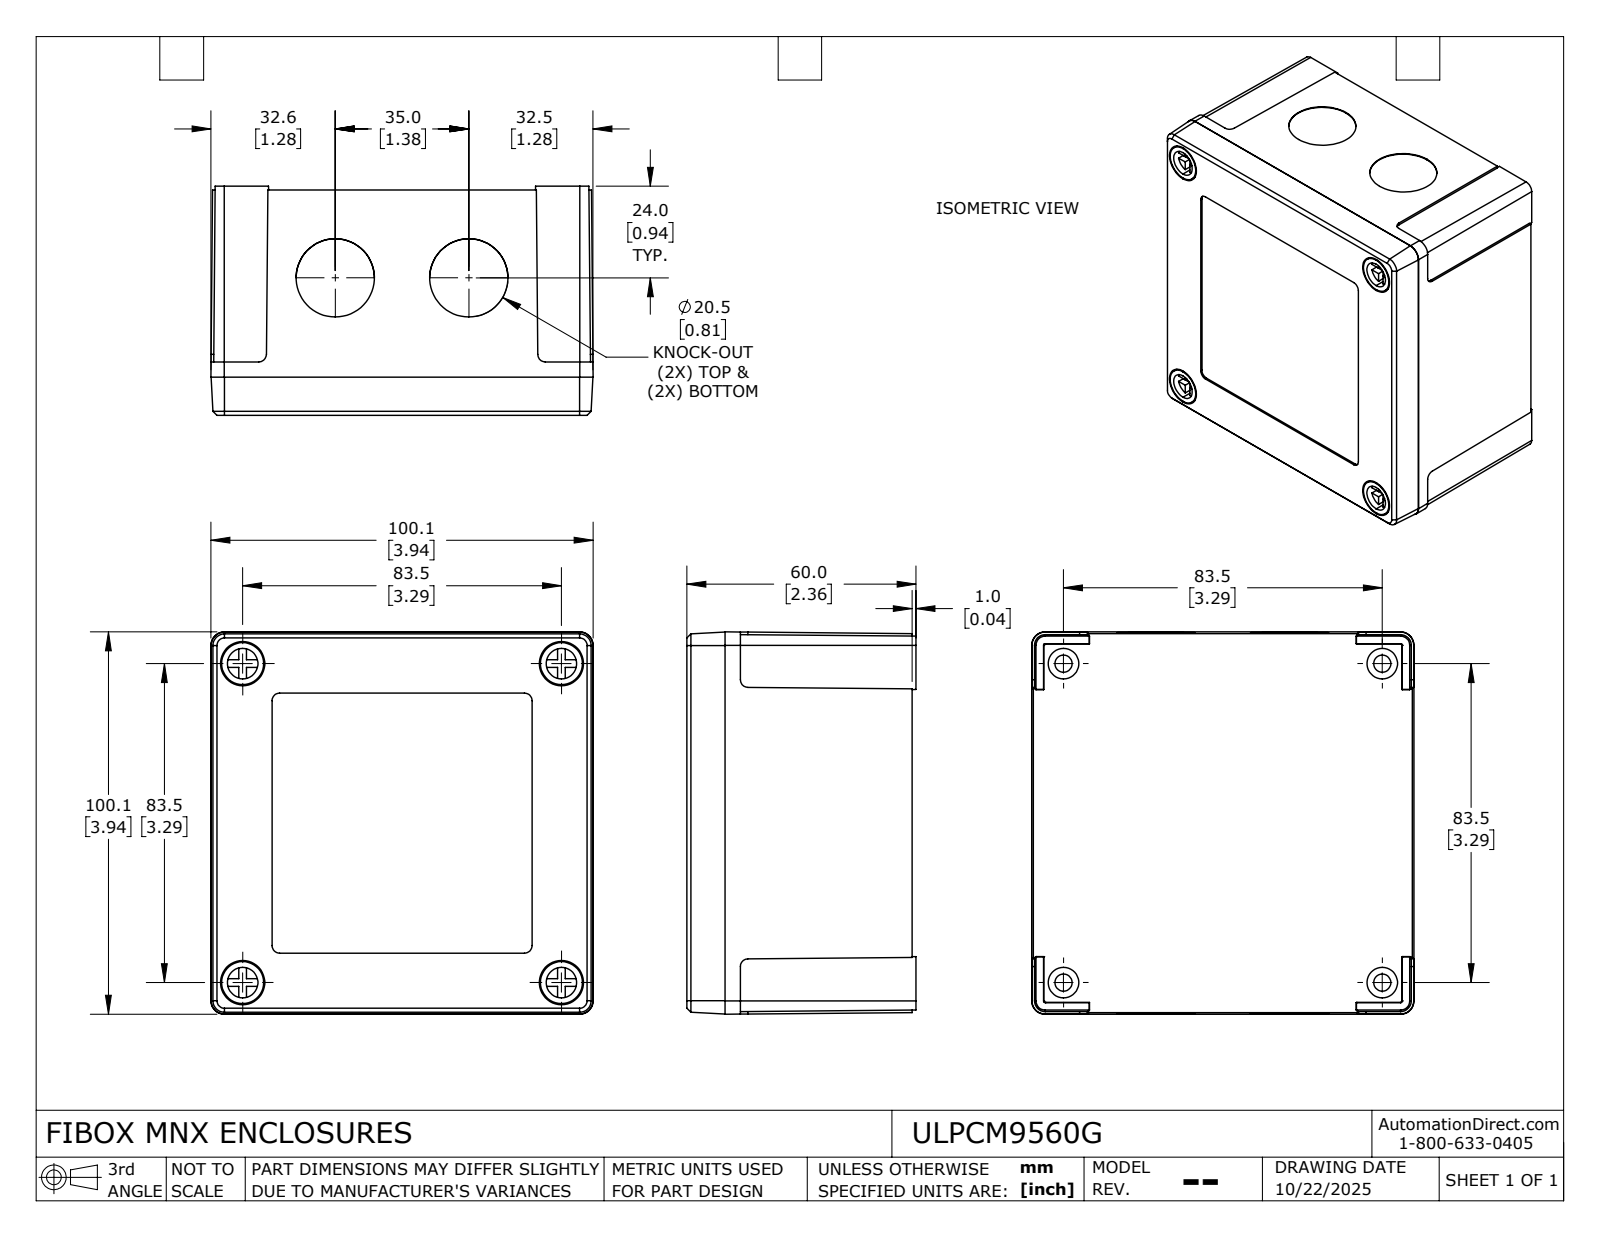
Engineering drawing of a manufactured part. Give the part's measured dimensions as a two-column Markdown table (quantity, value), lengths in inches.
| quantity | value |
| --- | --- |
| part name | ULPCM9560G_Default |
| STEP written by | SolidWorks 2024 (CONFIG_CONTROL_DESIGN) |
| units | inches |
| bodies | 6 solids, 510 faces (294 planar, 176 cylindrical, 40 other) |
| overall size | 3.941 × 3.941 × 2.362 |
| volume | 9.632 in³ |
| surface area | 147.4 in² |
| round holes (diameter × count) | 0.094 × 6, 0.118 × 6, 0.126 × 6, 0.157 × 6, 0.177 × 4, 0.315 × 4, 0.457 × 4, 0.807 × 4 |
| round bosses / shafts (diameter × count) | 0.315 × 6, 0.433 × 4, 0.283 × 4, 0.236 × 2 |
| partial cylindrical surfaces (radius × count) | 0.079 × 8, 0.056 × 6, 0.021 × 4, 0.03 × 4, 0.118 × 4, 0.197 × 4, 0.023 × 2 |
| main face-to-face distances | 0.165, 0.118, 2.232, 2.114, 2.205, 0.02, 2.303, 2.185, 0.071, 1.929 |
| hole center spacings | 0.803, 0.886, 1.159, 1.354, 1.461, 1.665, 1.824, 1.931 |
